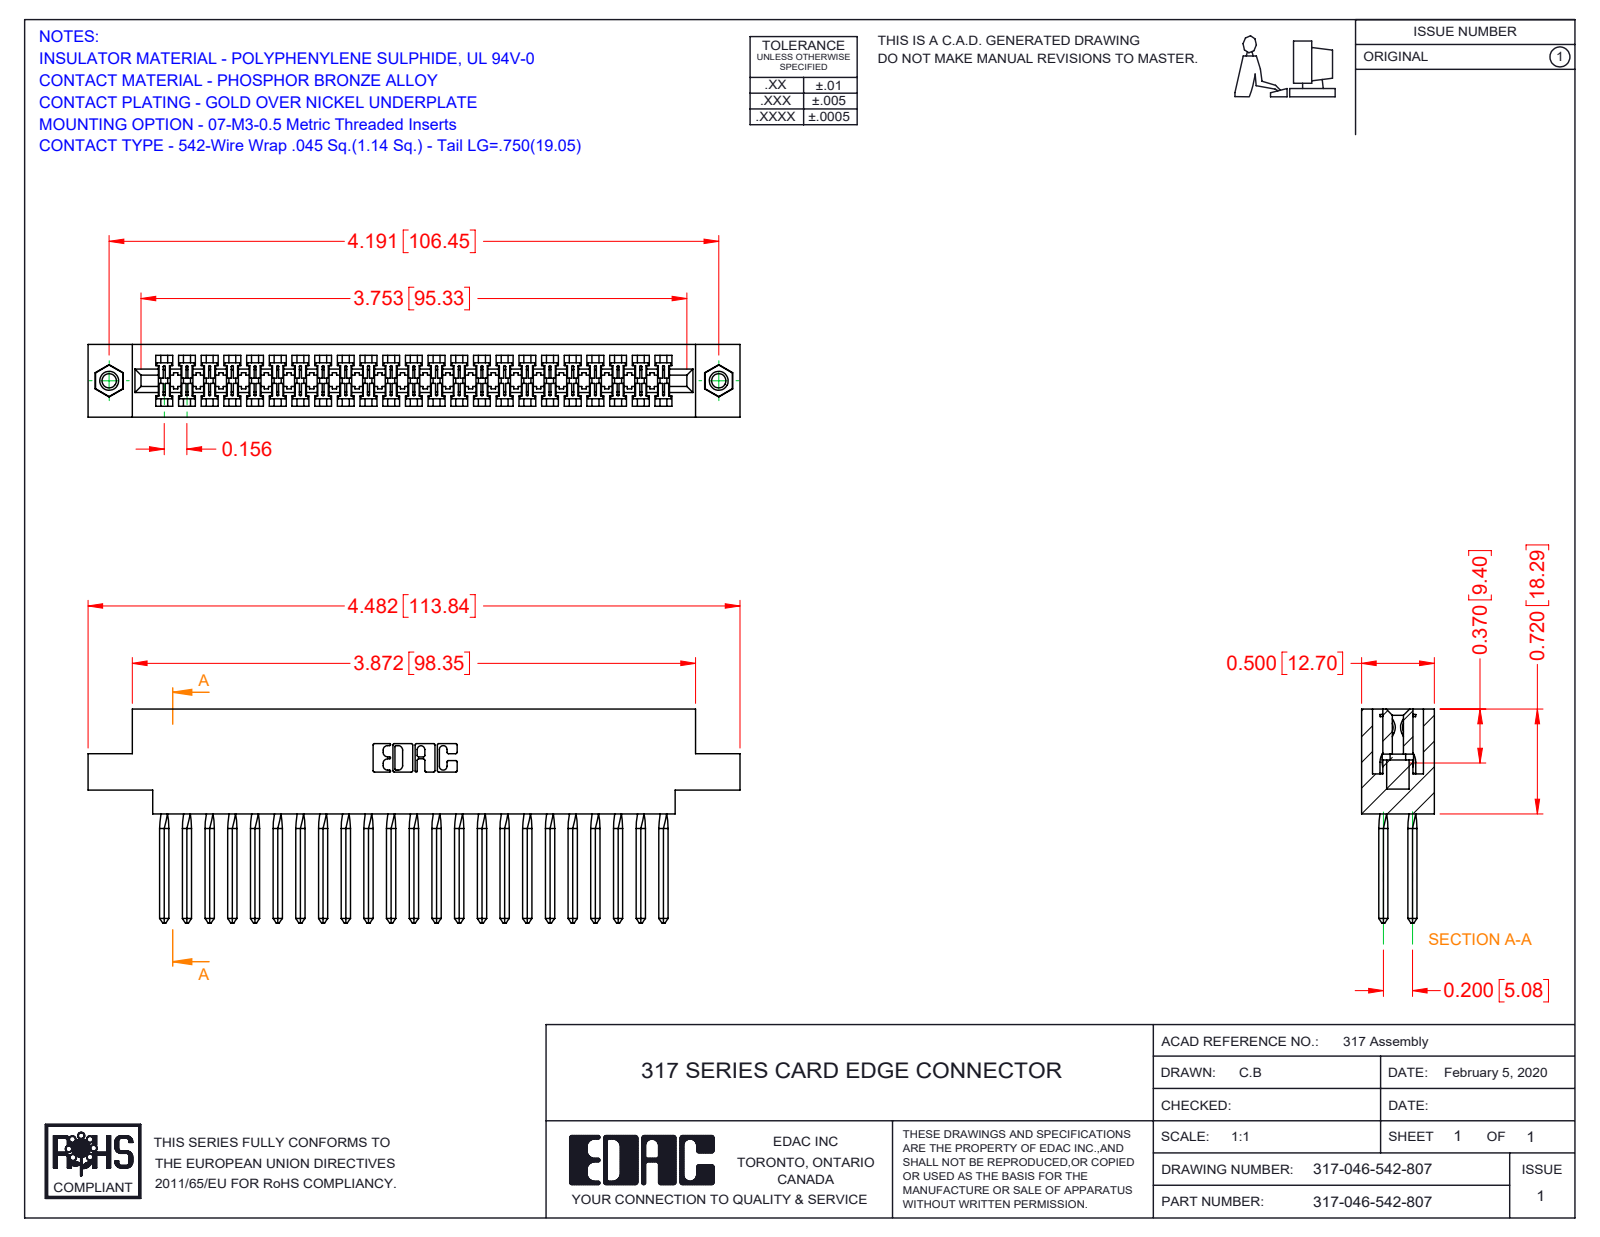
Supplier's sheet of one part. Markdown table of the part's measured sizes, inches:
| quantity | value |
| --- | --- |
| part name | 317 Part_.156 Dia - TI; 317-046-542-807; 317-290-003_542; 345-250-001_345-250-005-103 |
| STEP written by | SolidWorks 2016 (CONFIG_CONTROL_DESIGN) |
| units | inches |
| bodies | 49 solids, 2784 faces (2206 planar, 378 cylindrical, 200 other) |
| overall size | 4.482 × 1.47 × 0.5 |
| volume | 1.1 in³ |
| surface area | 37.97 in² |
| round holes (diameter × count) | 0.098 × 2, 0.125 × 2, 0.156 × 2 |
| round bosses / shafts (diameter × count) | 0.155 × 2 |
| partial cylindrical surfaces (radius × count) | 0.006 × 92, 0.01 × 22, 0.007 × 6, 0.031 × 6, 0.026 × 3, 0.074 × 2, 0.089 × 2, 0.1 × 2 |
| main face-to-face distances | 0.5, 0.075, 0.425, 0.35, 0.11, 0.2, 0.116, 0.136, 0.046, 0.72 |
| hole center spacings | 4.191 |
